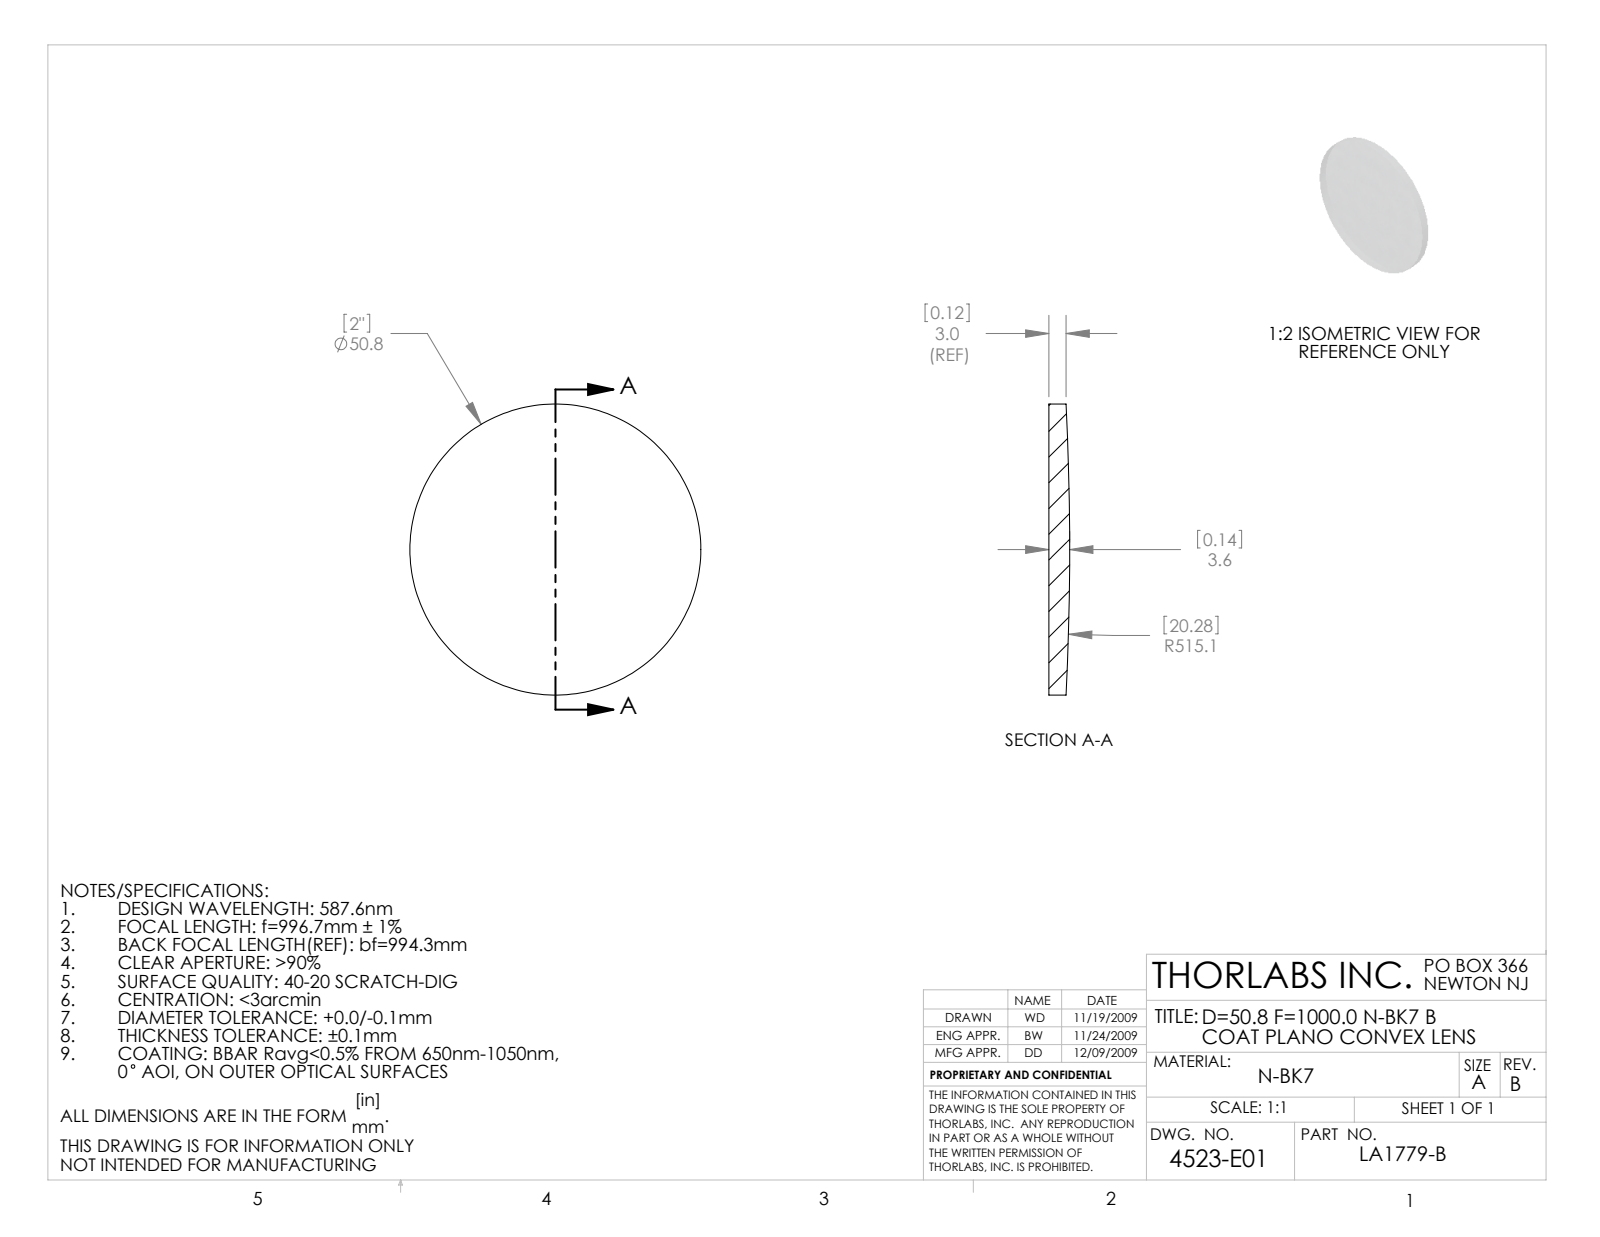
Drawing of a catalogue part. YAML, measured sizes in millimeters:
part_name: "4523-E0W"
step_written_by: "SolidWorks 2009 (AUTOMOTIVE_DESIGN)"
units: millimeters
bodies: {solids: 1, faces: 5, planar: 1, cylindrical: 2, other: 2}
overall_size: [50.8, 50.8, 3.62]
volume: 6702
surface_area: 4533
round_bosses_or_shafts:
  - {diameter: 50.8, count: 1}
